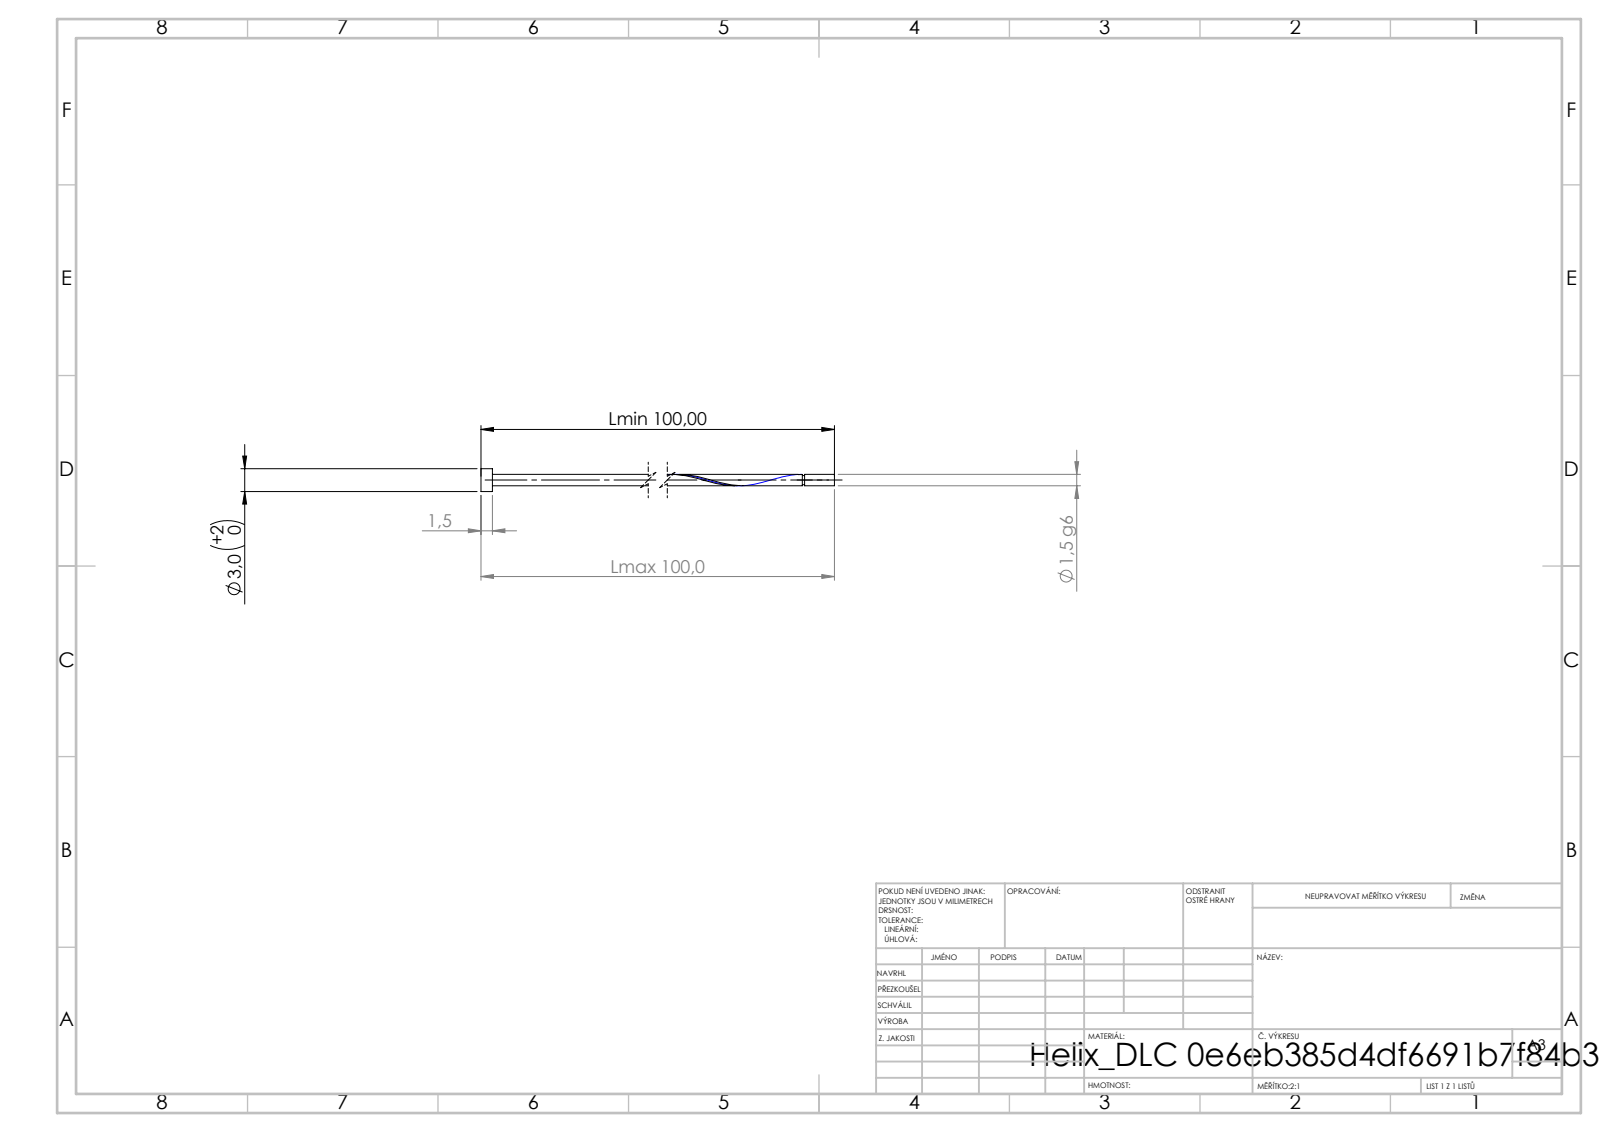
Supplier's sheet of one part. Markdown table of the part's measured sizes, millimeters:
| quantity | value |
| --- | --- |
| STEP written by | SolidWorks 2019 (CONFIG_CONTROL_DESIGN) |
| units | millimeters |
| bodies | 1 solid, 16 faces (6 planar, 9 cylindrical, 1 other) |
| overall size | 100 × 3 × 3 |
| volume | 222 mm³ |
| surface area | 658 mm² |
| round bosses / shafts (diameter × count) | 3 × 1, 1.5 × 1, 1.2 × 1 |
| main face-to-face distances | 1.5, 100, 98.5, 96.09, 94.59, 3.91, 95.79, 94.29, 4.21, 45.79 |
